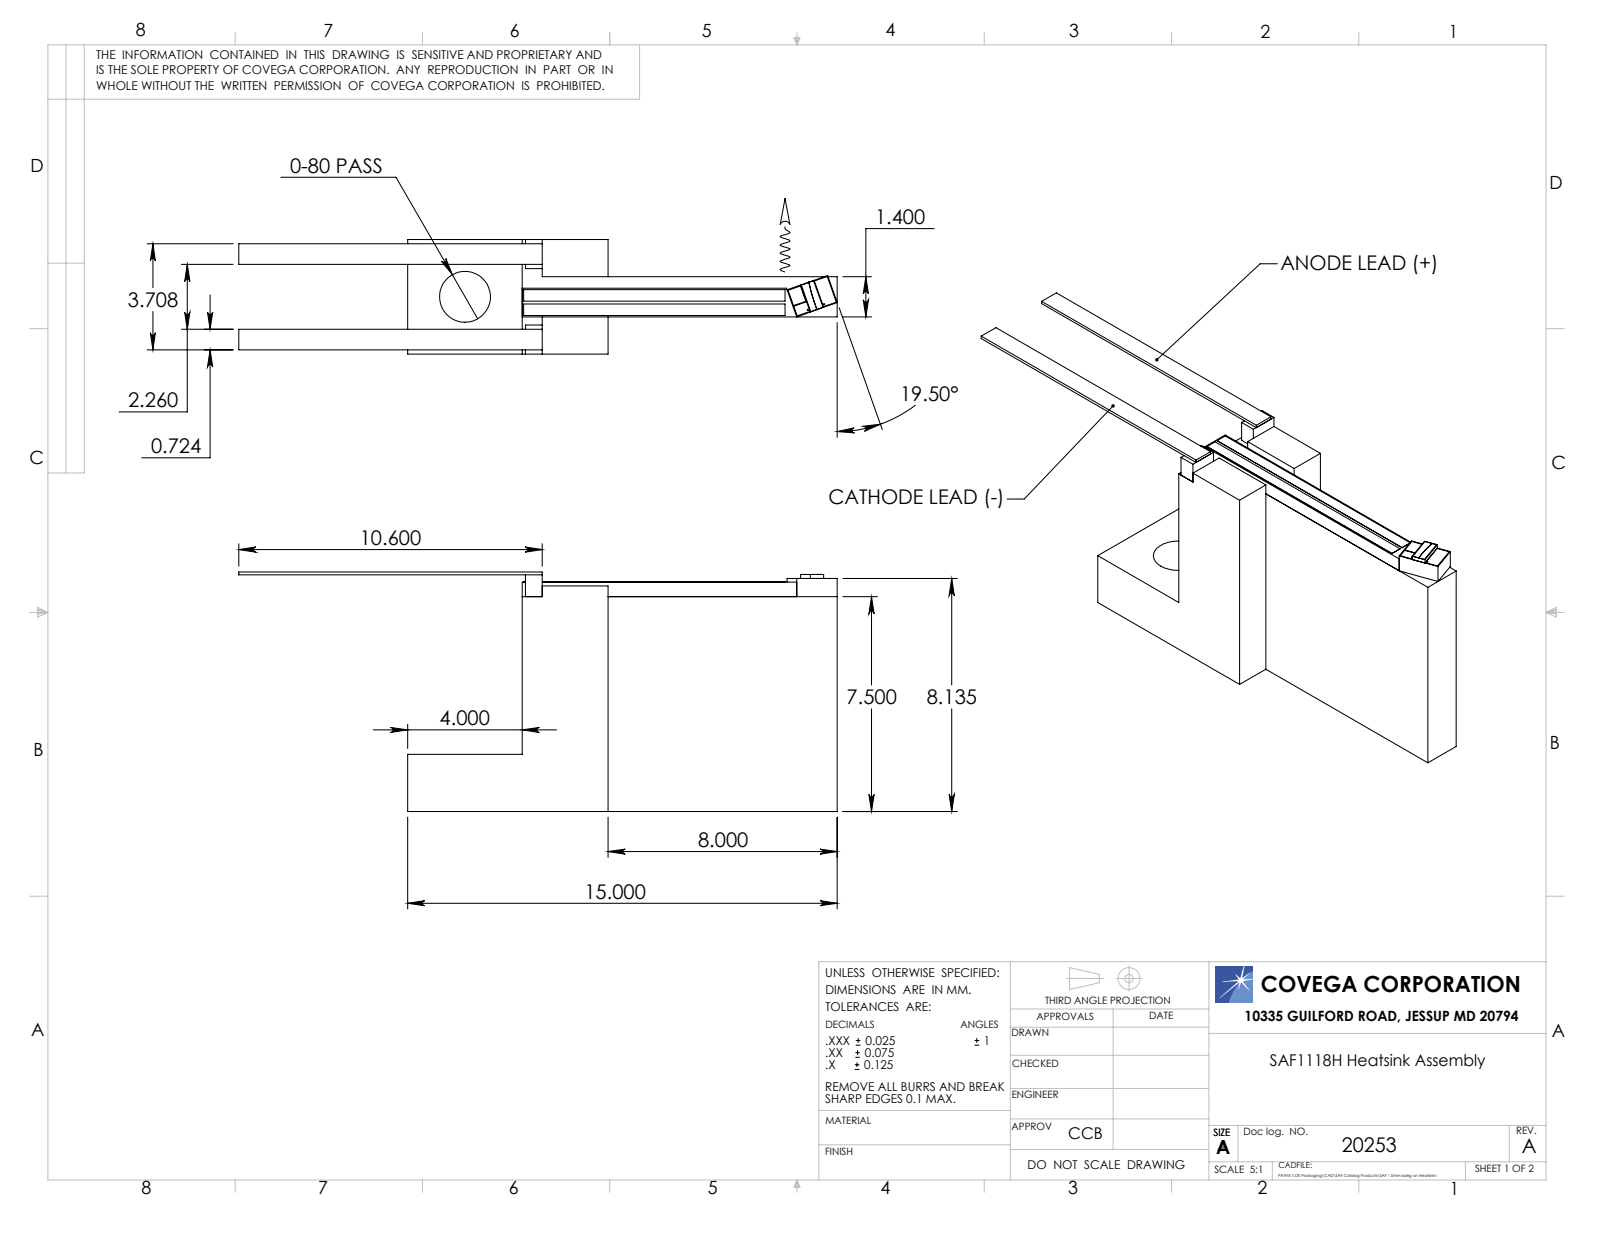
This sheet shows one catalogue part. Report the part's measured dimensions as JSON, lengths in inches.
{"part_name": "32139-000; PM-00068; 20253; 32138-000 (+6 more)", "step_written_by": "SolidWorks 2009 (AUTOMOTIVE_DESIGN)", "units": "inches", "bodies": {"solids": 8, "faces": 86, "planar": 84, "cylindrical": 2, "other": 0}, "overall_size": [0.823, 0.329, 0.157], "volume_in3": 0.013, "surface_area_in2": 0.637, "round_holes": [[0.07, 1]], "face_to_face_distances": [0.051, 0.106, 0.055, 0.157, 0.295, 0.118, 0.325, 0.03, 0.329, 0.034]}
